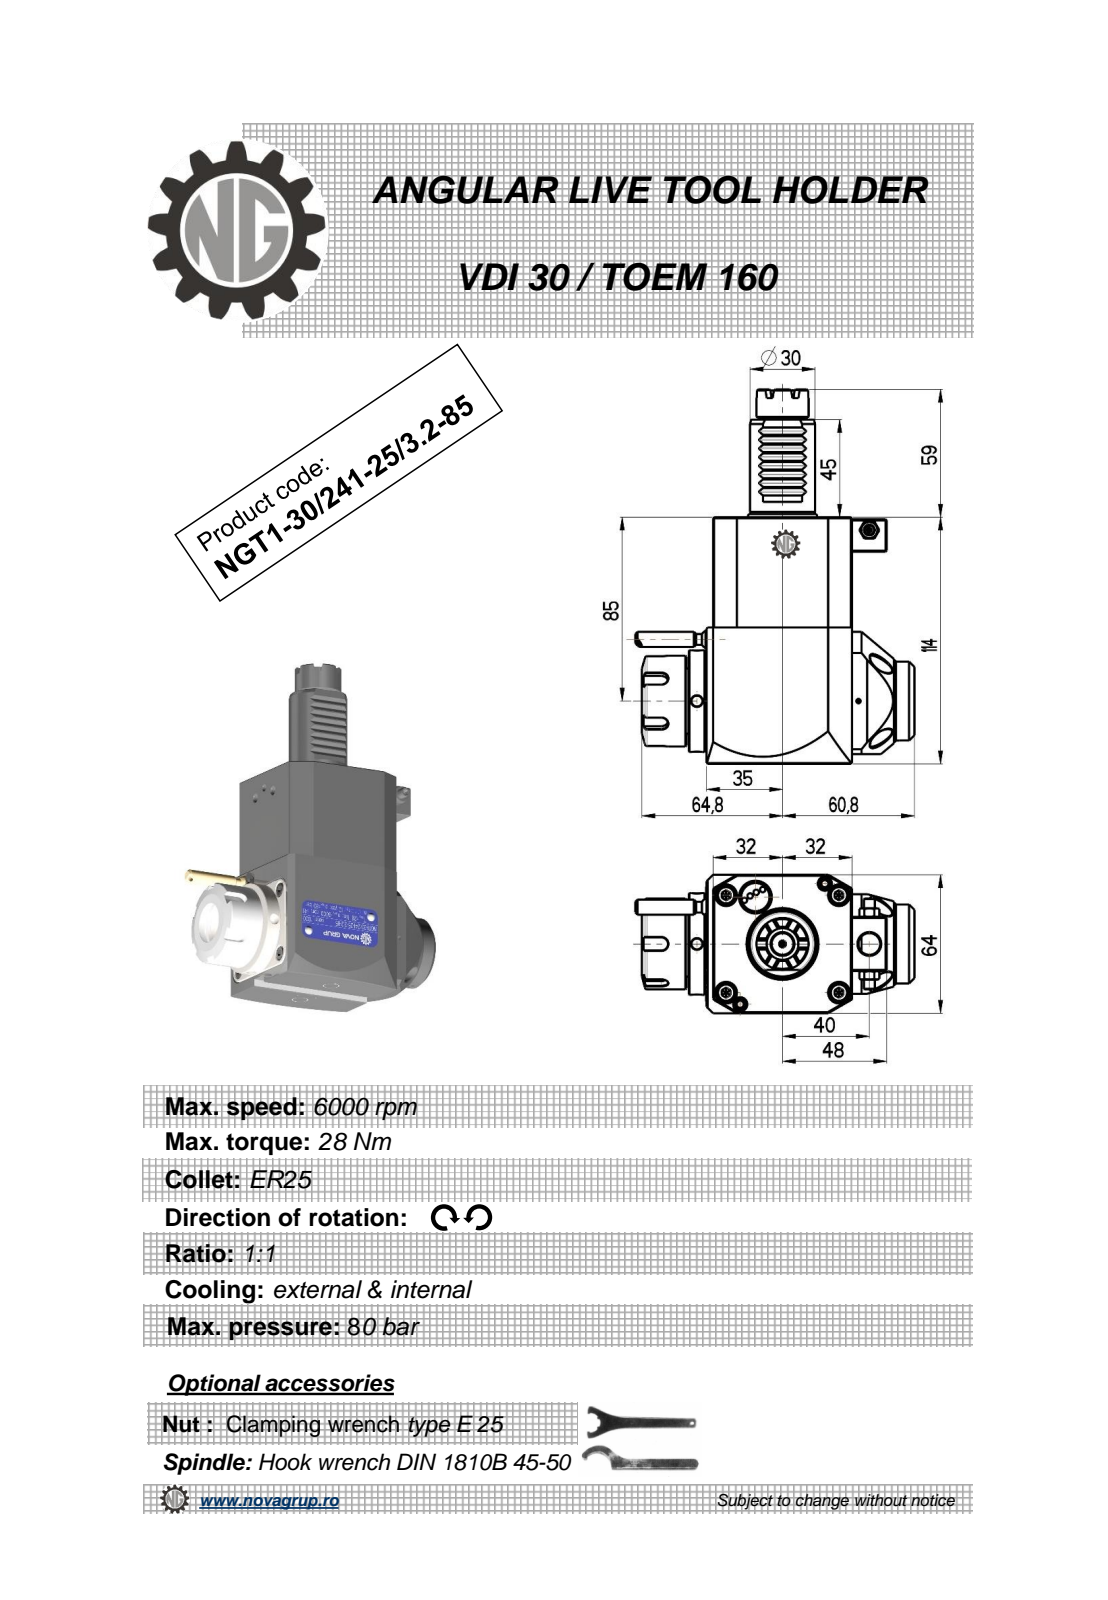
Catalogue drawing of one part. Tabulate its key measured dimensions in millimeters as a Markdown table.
| quantity | value |
| --- | --- |
| part name | NGT1_30_241_25_3_2_85 |
| STEP written by | PRO/ENGINEER BY PARAMETRIC TECHNOLOGY CORPORATION, 2010280 (CONFIG_CONTROL_DESIGN) |
| units | millimeters |
| bodies | 1 solid, 457 faces (213 planar, 86 cylindrical, 158 other) |
| overall size | 173 × 128.63 × 64 |
| volume | 592 671 mm³ |
| surface area | 55 818 mm² |
| round holes (diameter × count) | 5 × 2, 2.5 × 1, 3 × 1, 4.2 × 1, 9.5 × 1, 10 × 1, 20.3 × 1 |
| round bosses / shafts (diameter × count) | 5 × 2, 47 × 1, 42 × 1, 36.5 × 1, 35 × 1, 30 × 1, 24 × 1, 17.7 × 1 |
| partial cylindrical surfaces (radius × count) | 0.26 × 12, 0.3 × 8, 3 × 5, 160 × 2, 7.6 × 1, 32 × 1 |
| main face-to-face distances | 64, 114, 0.5, 3.2, 67.2, 76.42, 67, 3, 7.5, 96 |
| hole center spacings | 33.19, 50.92, 76.5, 79.45, 112.04 |
